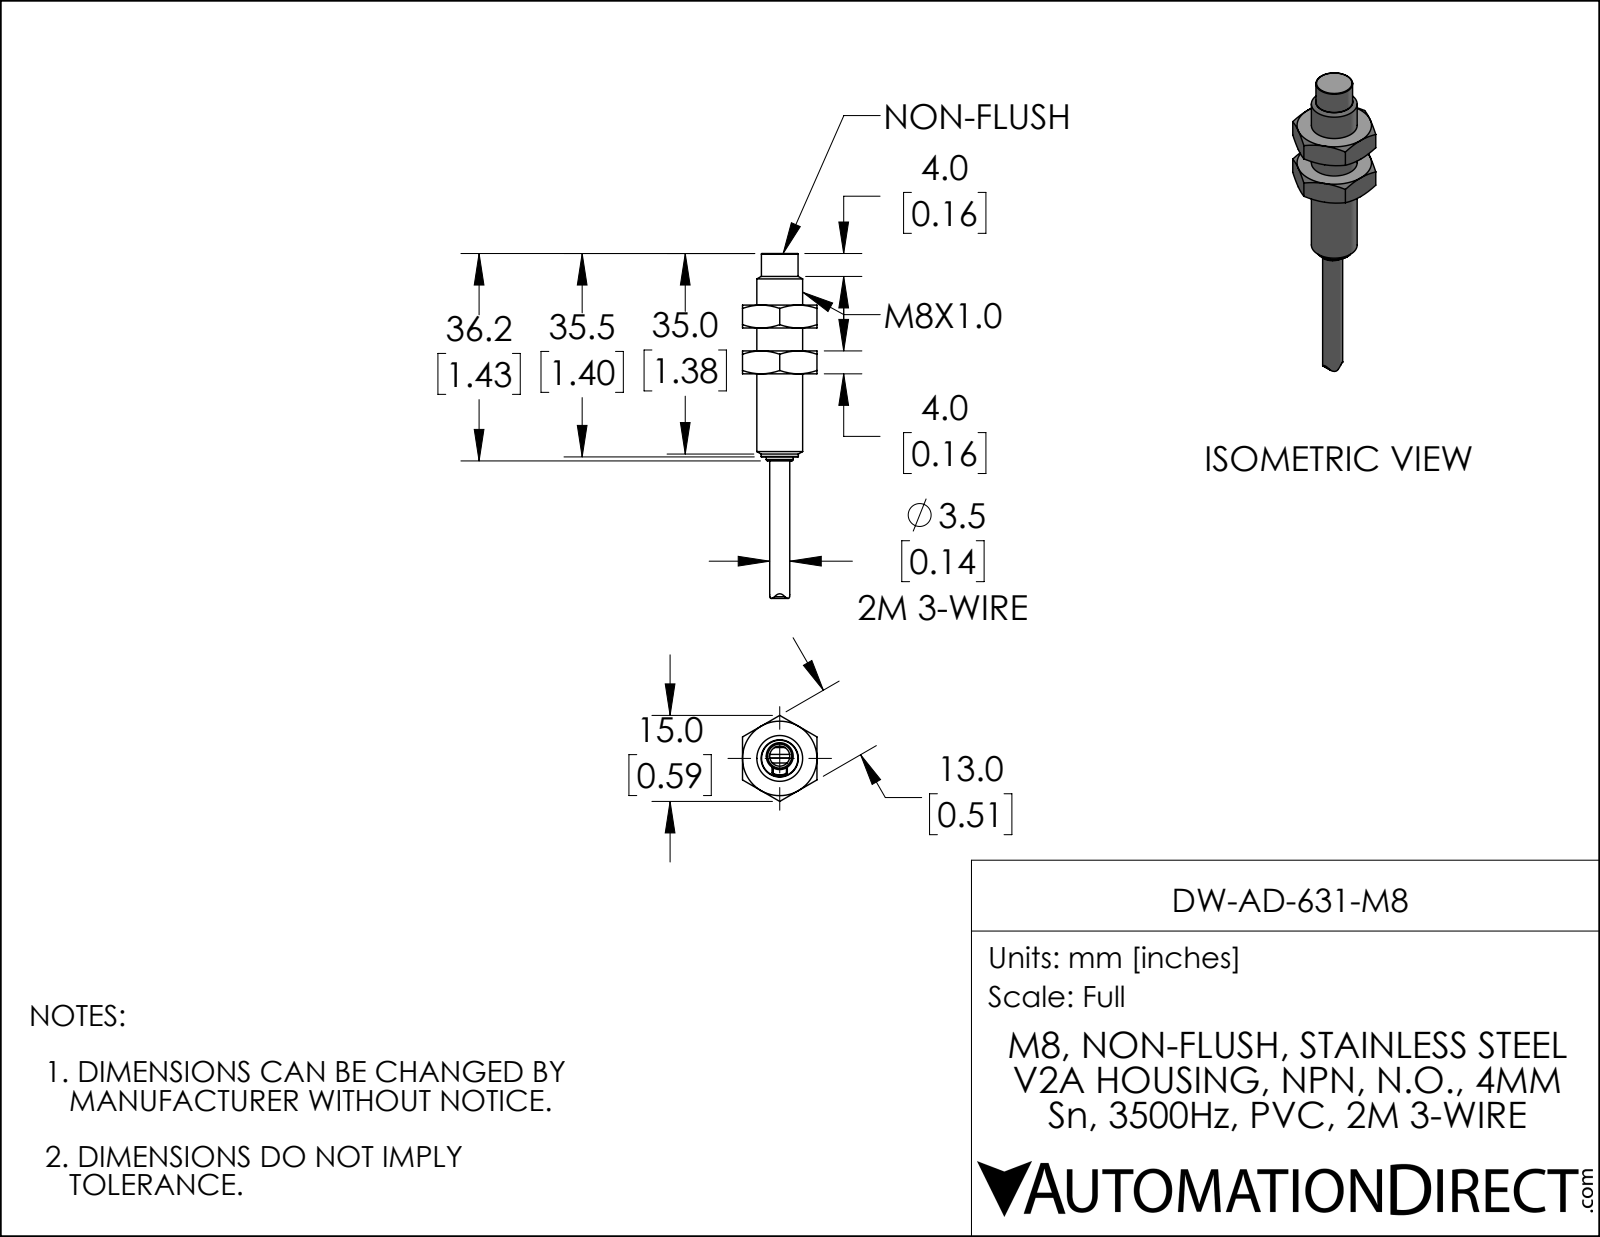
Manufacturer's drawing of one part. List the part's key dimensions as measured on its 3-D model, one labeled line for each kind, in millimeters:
Part name (STEP PRODUCT): DW-AD-631-M8
STEP written by: SolidWorks 2019 (AUTOMOTIVE_DESIGN)
Units: millimetres
Bodies: 1 solid, 78 faces (23 planar, 19 cylindrical, 36 other)
Overall size (bounding box): 60.2 × 15 × 13
Volume: 2 690 mm³ · Surface area: 1 739 mm²
Round bosses / shafts (diameter × count): ⌀8 ×1, ⌀6.5 ×1, ⌀6.4 ×1, ⌀4.7 ×1, ⌀3.5 ×1
Partial cylindrical surfaces — rounded edges, fillets, slot ends (radius × count): R0.3 ×2, R0.6 ×1, R0.8 ×1, R2.9 ×1, R3 ×1, R4.5 ×1, R6 ×1
Main face-to-face distances: 4, 13, 8, 12, 9, 17, 21, 35.5, 26.5, 22.5
